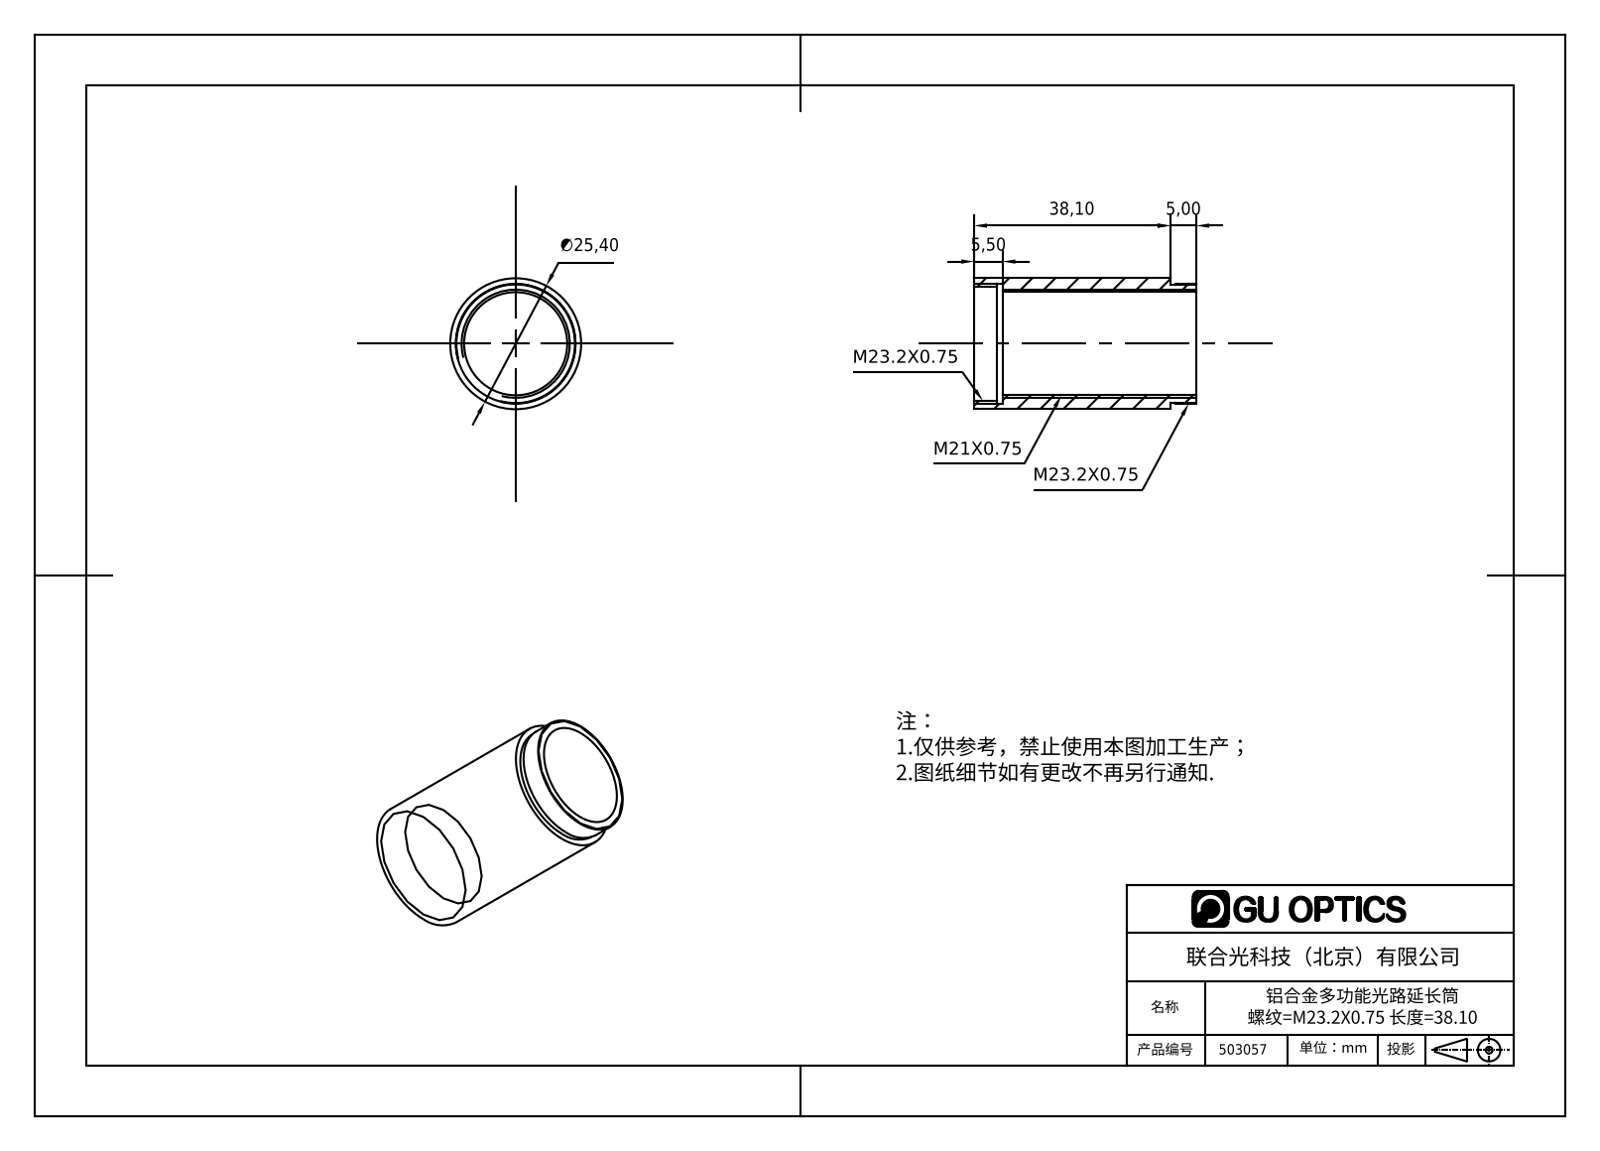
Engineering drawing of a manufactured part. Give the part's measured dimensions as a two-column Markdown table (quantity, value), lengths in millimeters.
| quantity | value |
| --- | --- |
| part name | 503057 |
| STEP written by | SolidWorks 2016 (AUTOMOTIVE_DESIGN) |
| units | millimeters |
| bodies | 1 solid, 18 faces (6 planar, 12 cylindrical, 0 other) |
| overall size | 43.1 × 25.4 × 25.4 |
| volume | 7 428 mm³ |
| surface area | 6 639 mm² |
| round holes (diameter × count) | 20 × 1, 22.2 × 1, 23.4 × 1 |
| round bosses / shafts (diameter × count) | 25.4 × 1, 23.2 × 1, 23 × 1 |
| main face-to-face distances | 5.5, 43.1, 37.6, 38.1, 32.6, 5, 1, 33.6, 4.5, 38.6 |
